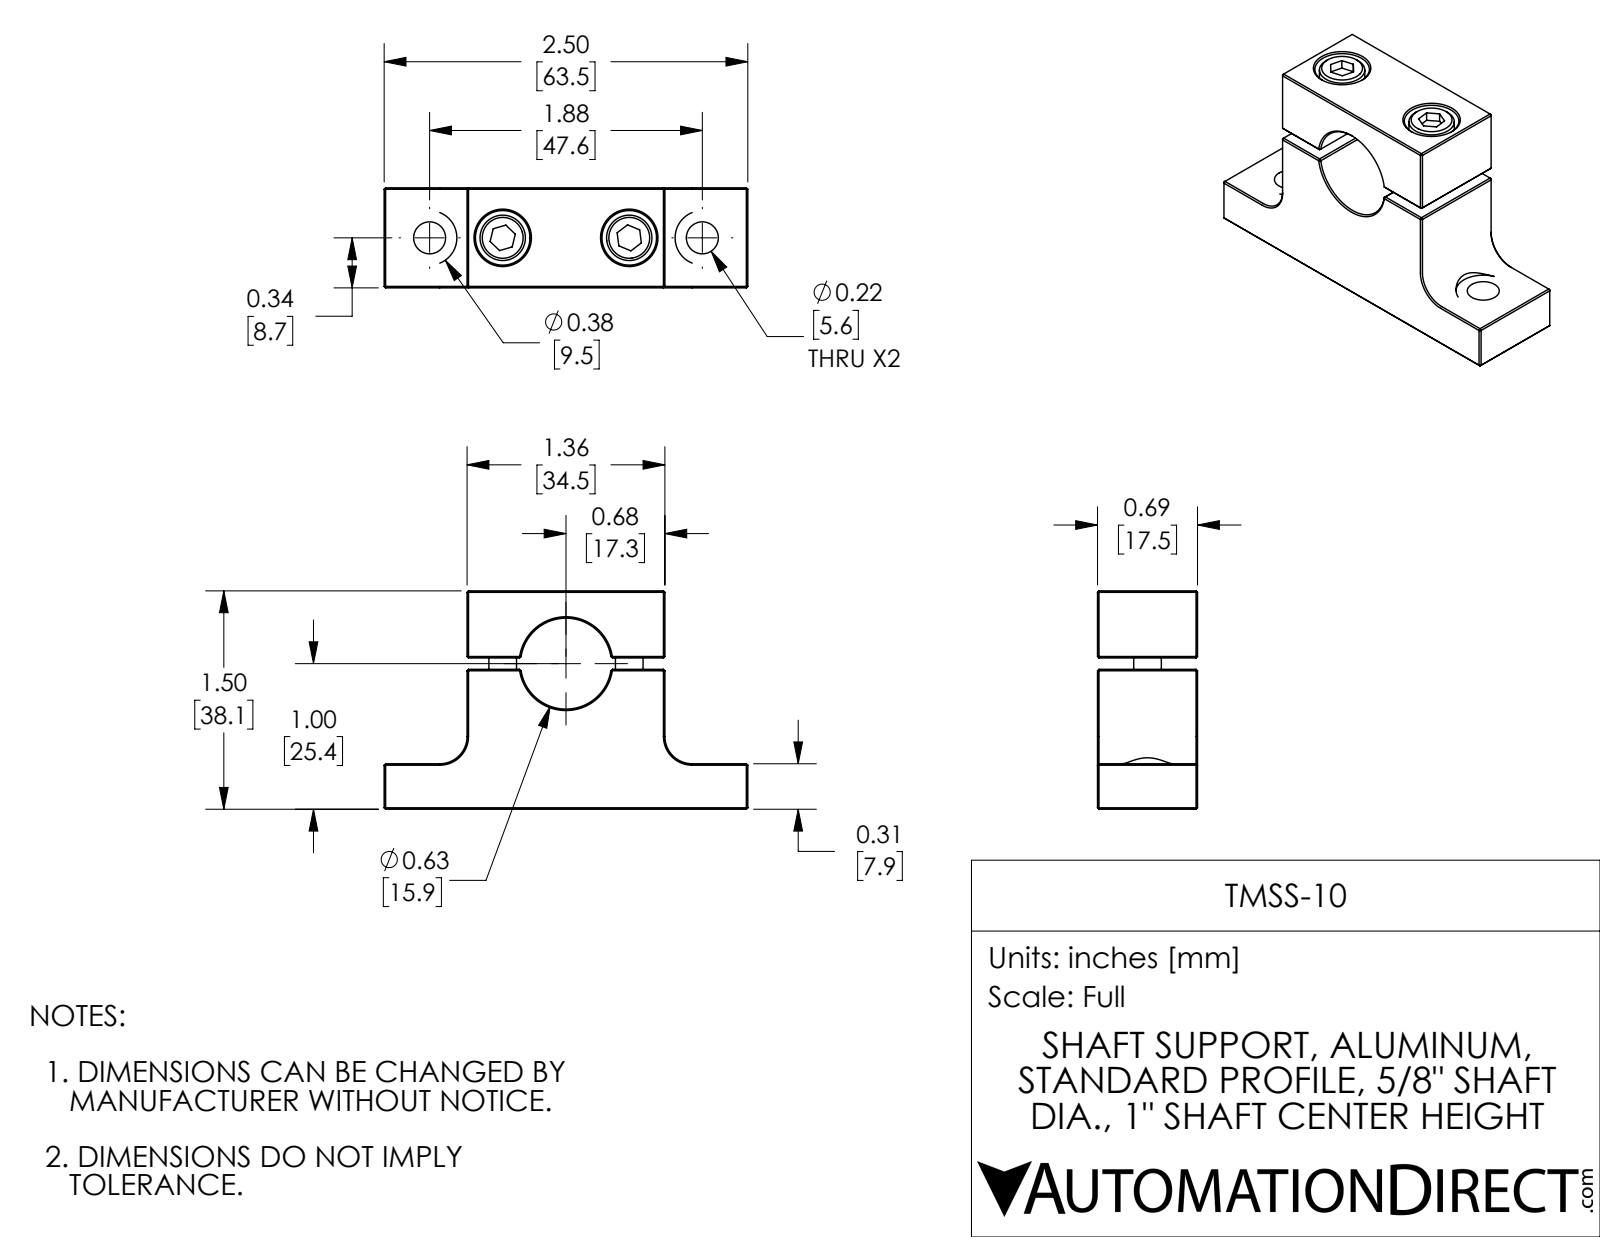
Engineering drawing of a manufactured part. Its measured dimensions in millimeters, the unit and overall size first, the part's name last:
Units: millimetres
Overall size (bounding box): 63.5 × 38.1 × 17.5
Round holes (diameter × count): ⌀3.7 ×2, ⌀5.1 ×2, ⌀5.6 ×2, ⌀9.5 ×2, ⌀15.9 ×1
Round bosses / shafts (diameter × count): ⌀7.9 ×2, ⌀4.8 ×2
Partial cylindrical surfaces — rounded edges, fillets, slot ends (radius × count): R4.7 ×4
Main face-to-face distances: 17.4, 38.1, 34.5, 7.9, 30.2, 24.4, 16.5, 13.7, 26.4, 18.5
Hole centre spacings: 12.8, 34.8, 22.1, 47.6
Volume: 22 270 mm³ · Surface area: 9 548 mm²
Bodies: 4 solids, 165 faces (110 planar, 31 cylindrical, 24 other)
Part name (STEP PRODUCT): TMSS-10
STEP written by: SolidWorks 2017 (AUTOMOTIVE_DESIGN)
